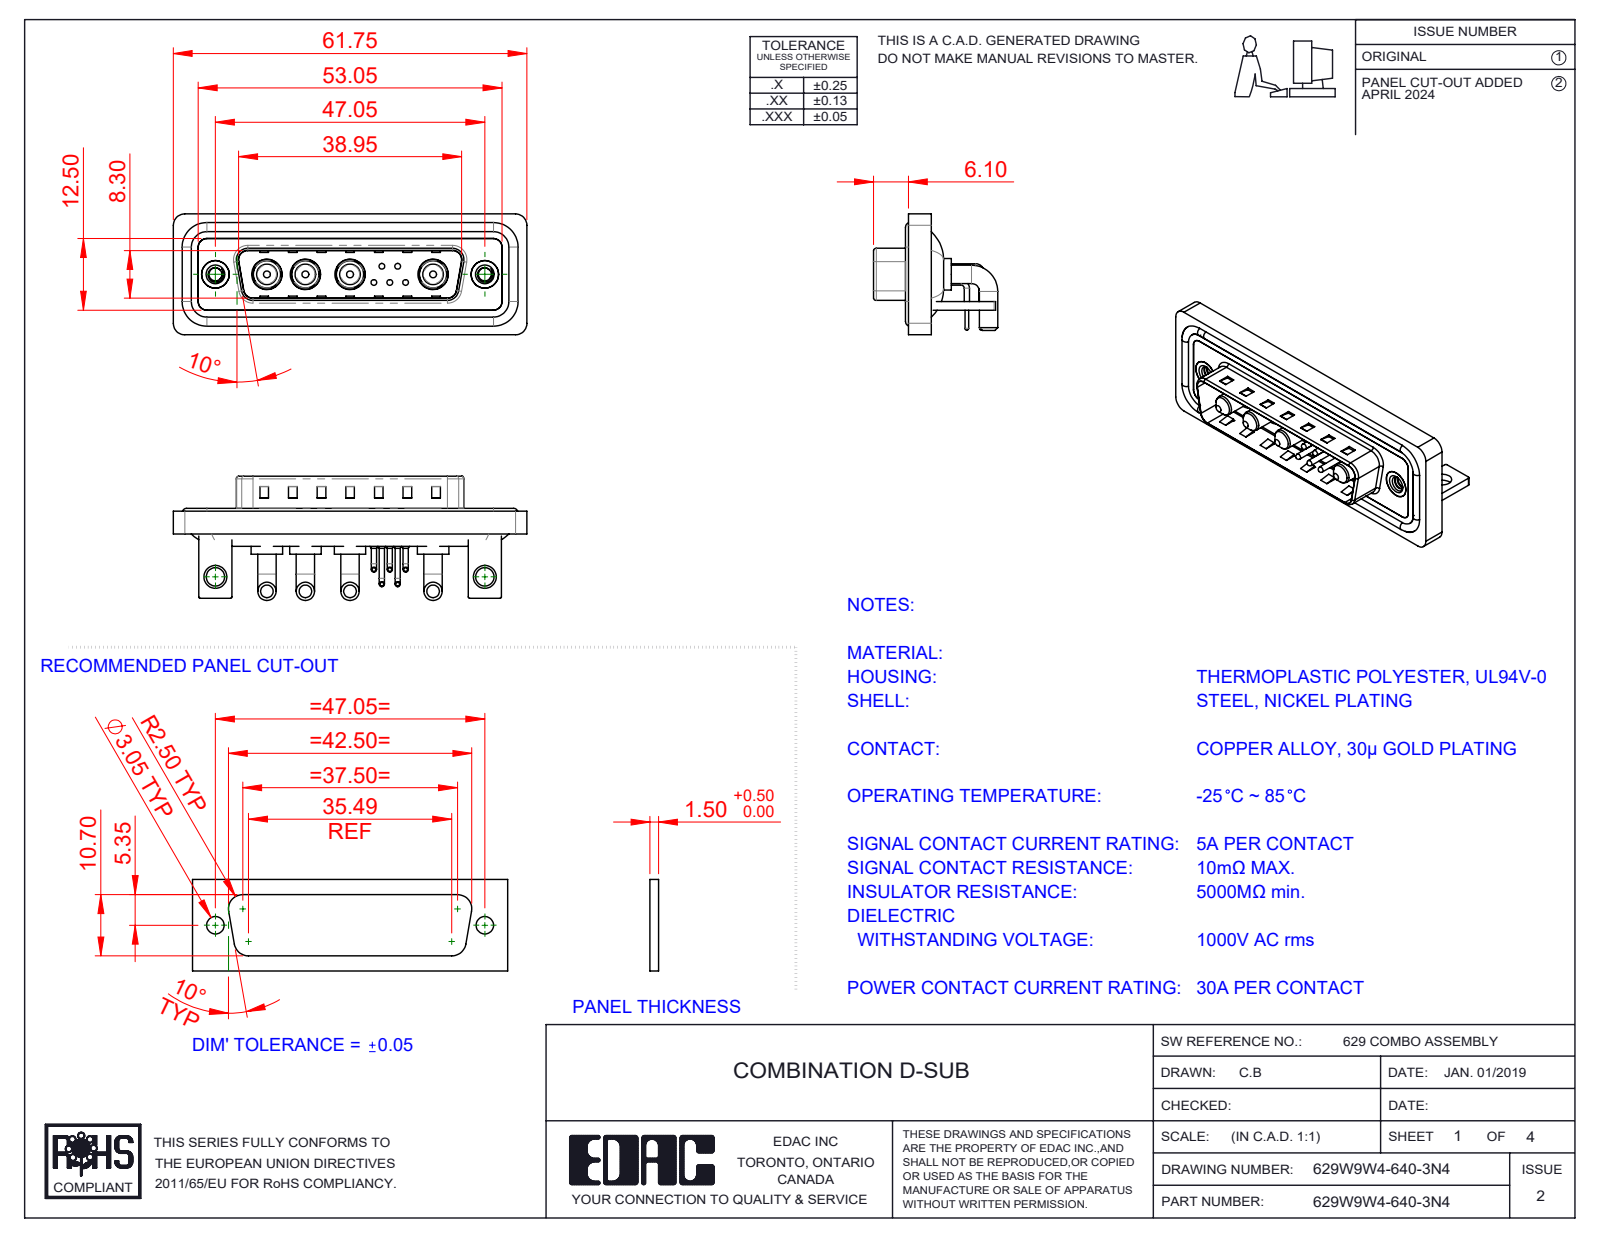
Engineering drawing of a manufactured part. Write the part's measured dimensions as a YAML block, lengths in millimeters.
part_name: "629W9W4-640-3N4; 629Combo Contact Row 2; 629Combo Shell Front_25 Contacts; Power Pin_30A RA (+6 more)"
step_written_by: "SolidWorks 2023 (CONFIG_CONTROL_DESIGN)"
units: millimeters
bodies: {solids: 22, faces: 1245, planar: 589, cylindrical: 470, other: 186}
overall_size: [61.75, 21.7, 21.1]
volume: 8094
surface_area: 13037
round_holes:
  - {diameter: 0.75, count: 5}
  - {diameter: 1.6, count: 5}
  - {diameter: 2, count: 5}
  - {diameter: 4.85, count: 4}
  - {diameter: 5.3, count: 4}
  - {diameter: 2.26, count: 2}
  - {diameter: 3.2, count: 2}
  - {diameter: 4, count: 2}
  - {diameter: 4.8, count: 2}
  - {diameter: 5, count: 2}
round_bosses_or_shafts:
  - {diameter: 0.9, count: 10}
  - {diameter: 3.2, count: 8}
  - {diameter: 1.5, count: 5}
  - {diameter: 1, count: 5}
  - {diameter: 0.65, count: 5}
  - {diameter: 5.5, count: 4}
  - {diameter: 5.2, count: 4}
  - {diameter: 4.75, count: 4}
partial_cylinders:
  - {radius: 2, count: 19}
  - {radius: 1.5, count: 18}
  - {radius: 0.25, count: 16}
  - {radius: 0.5, count: 9}
  - {radius: 1.6, count: 8}
  - {radius: 1.01, count: 5}
  - {radius: 0.6, count: 4}
  - {radius: 0.65, count: 4}
face_to_face_distances: [0.4, 1.5, 0.8, 2.9, 2.1, 1.1, 3.7, 4.1, 4.5, 1.6]
hole_center_spacings: [3.16, 2.77, 5.04, 14.5, 47.05, 2.78, 4.4, 4.41]
